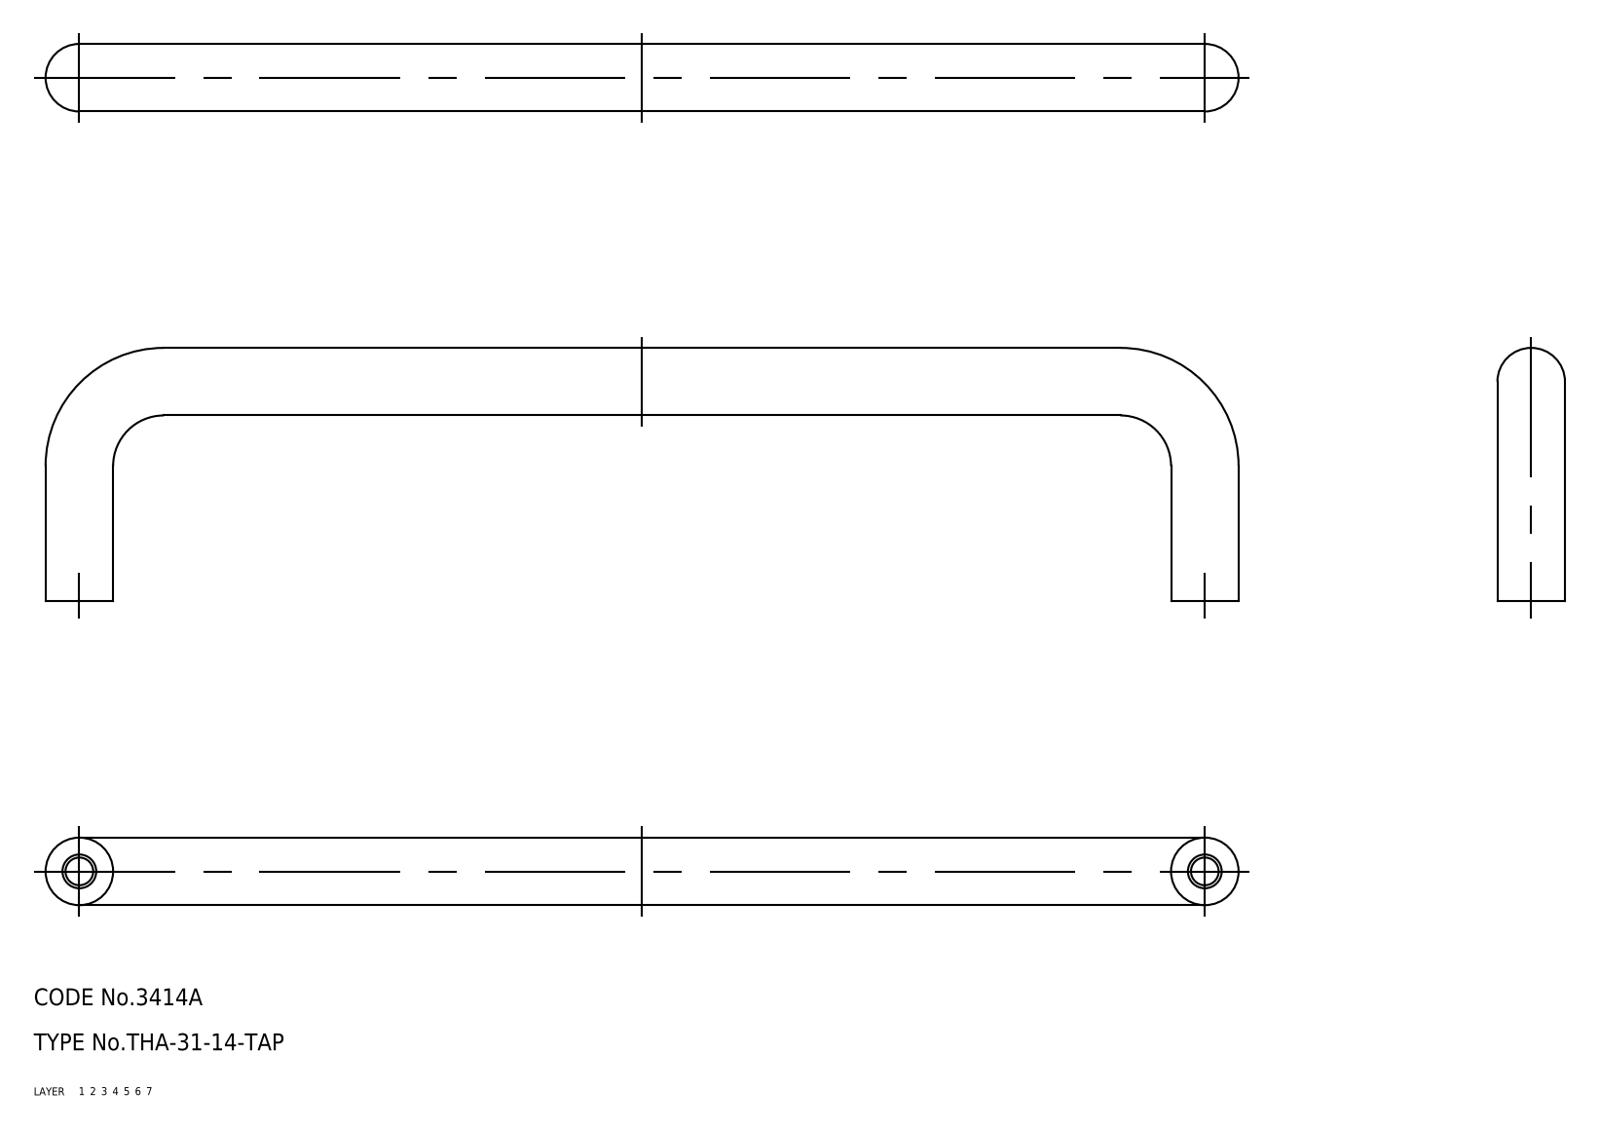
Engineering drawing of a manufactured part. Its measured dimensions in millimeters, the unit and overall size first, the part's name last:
Units: millimetres
Overall size (bounding box): 212 × 45 × 12
Volume: 28 968 mm³ · Surface area: 10 982 mm²
Bodies: 1 solid, 18 faces (0 planar, 0 cylindrical, 18 other)
Part name (STEP PRODUCT): pull
STEP written by: CADfix (AUTOMOTIVE_DESIGN)
